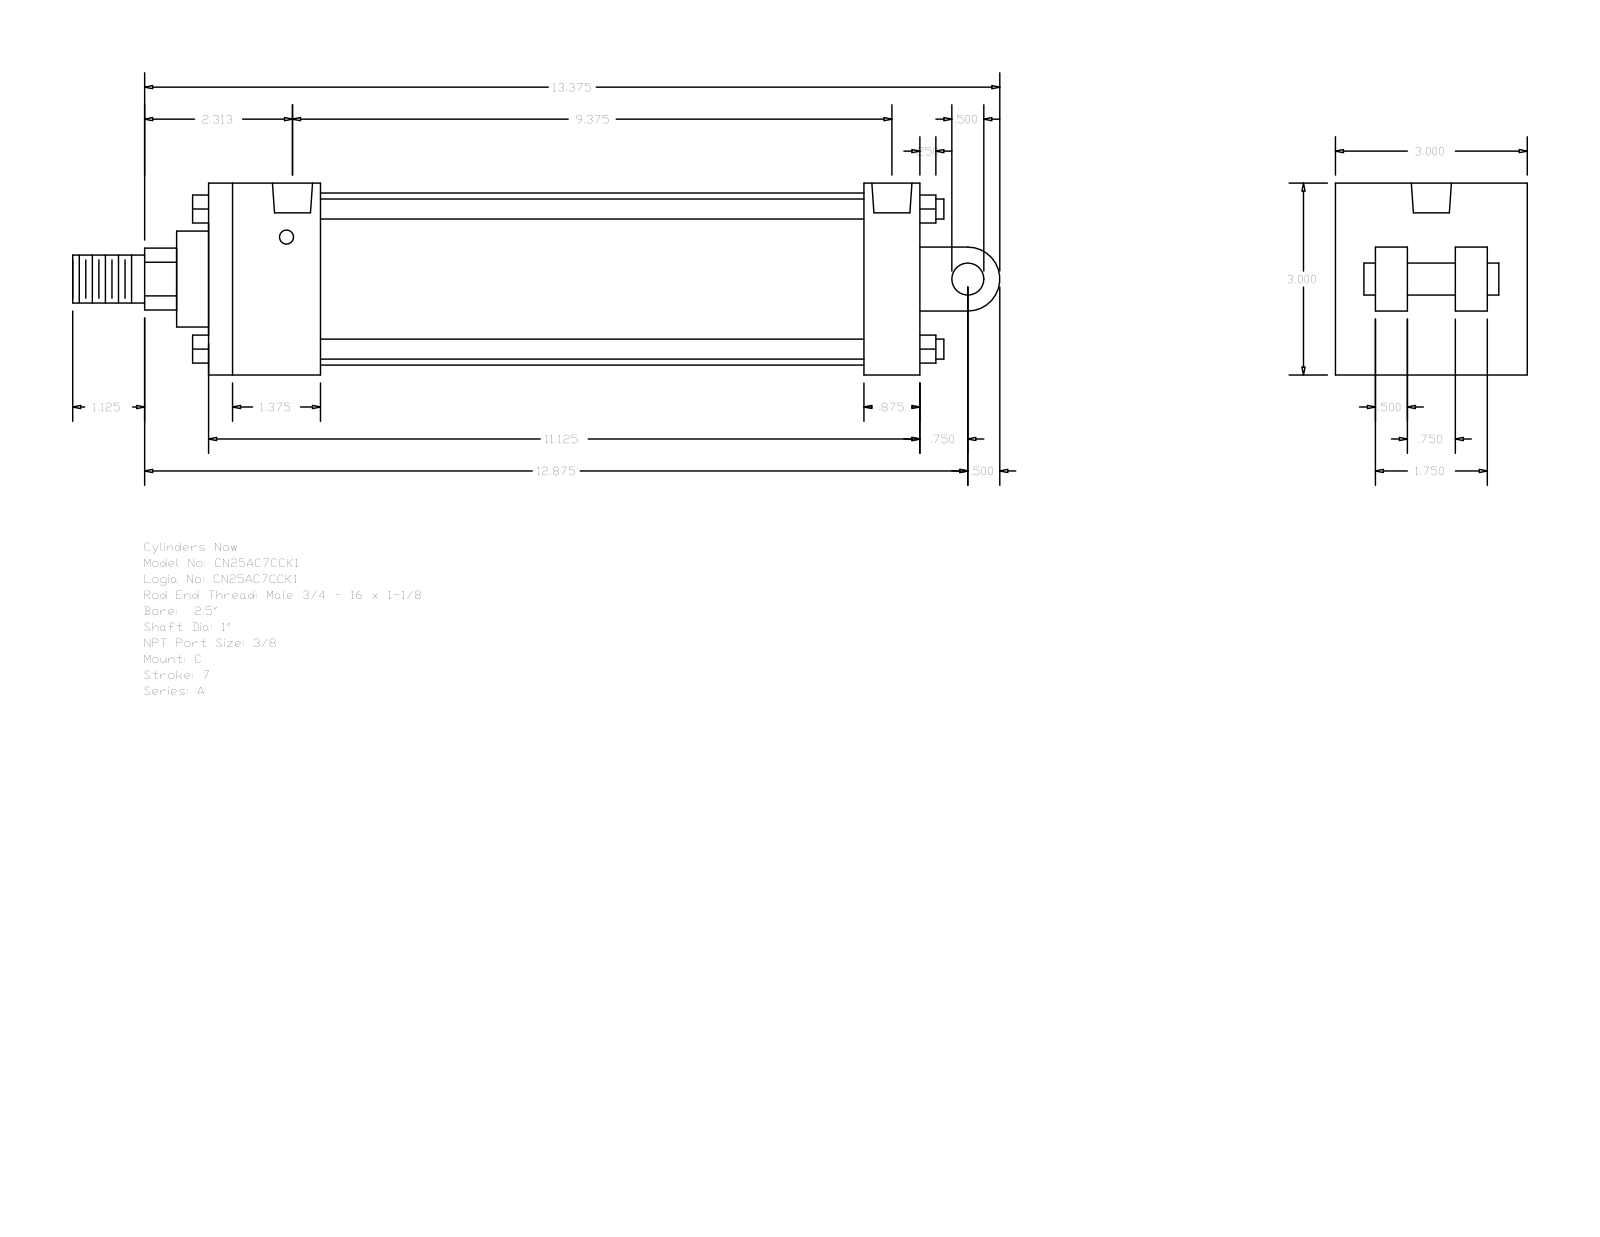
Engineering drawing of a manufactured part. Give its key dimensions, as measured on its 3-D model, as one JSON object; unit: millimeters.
{"part_name": "A_C__0250_1", "step_written_by": "GSSL Pune (CONFIG_CONTROL_DESIGN)", "units": "millimeters", "bodies": {"solids": 0, "faces": 135, "planar": 102, "cylindrical": 33, "other": 0}, "overall_size": [368.3, 76.2, 76.2], "round_holes": [[5.56, 4], [15.93, 2]], "round_bosses_or_shafts": [[7.94, 4], [68.33, 1], [38.1, 1], [25.4, 1], [19.05, 1], [12.7, 1]], "partial_cylinders_radius": [[12.29, 1], [12.7, 1]], "face_to_face_distances": [76.2, 282.58, 12.7, 44.45, 260.35, 215.9, 238.13, 22.23, 15.87, 25.4], "hole_center_spacings": [2.38, 240.5, 242.88, 238.12]}
